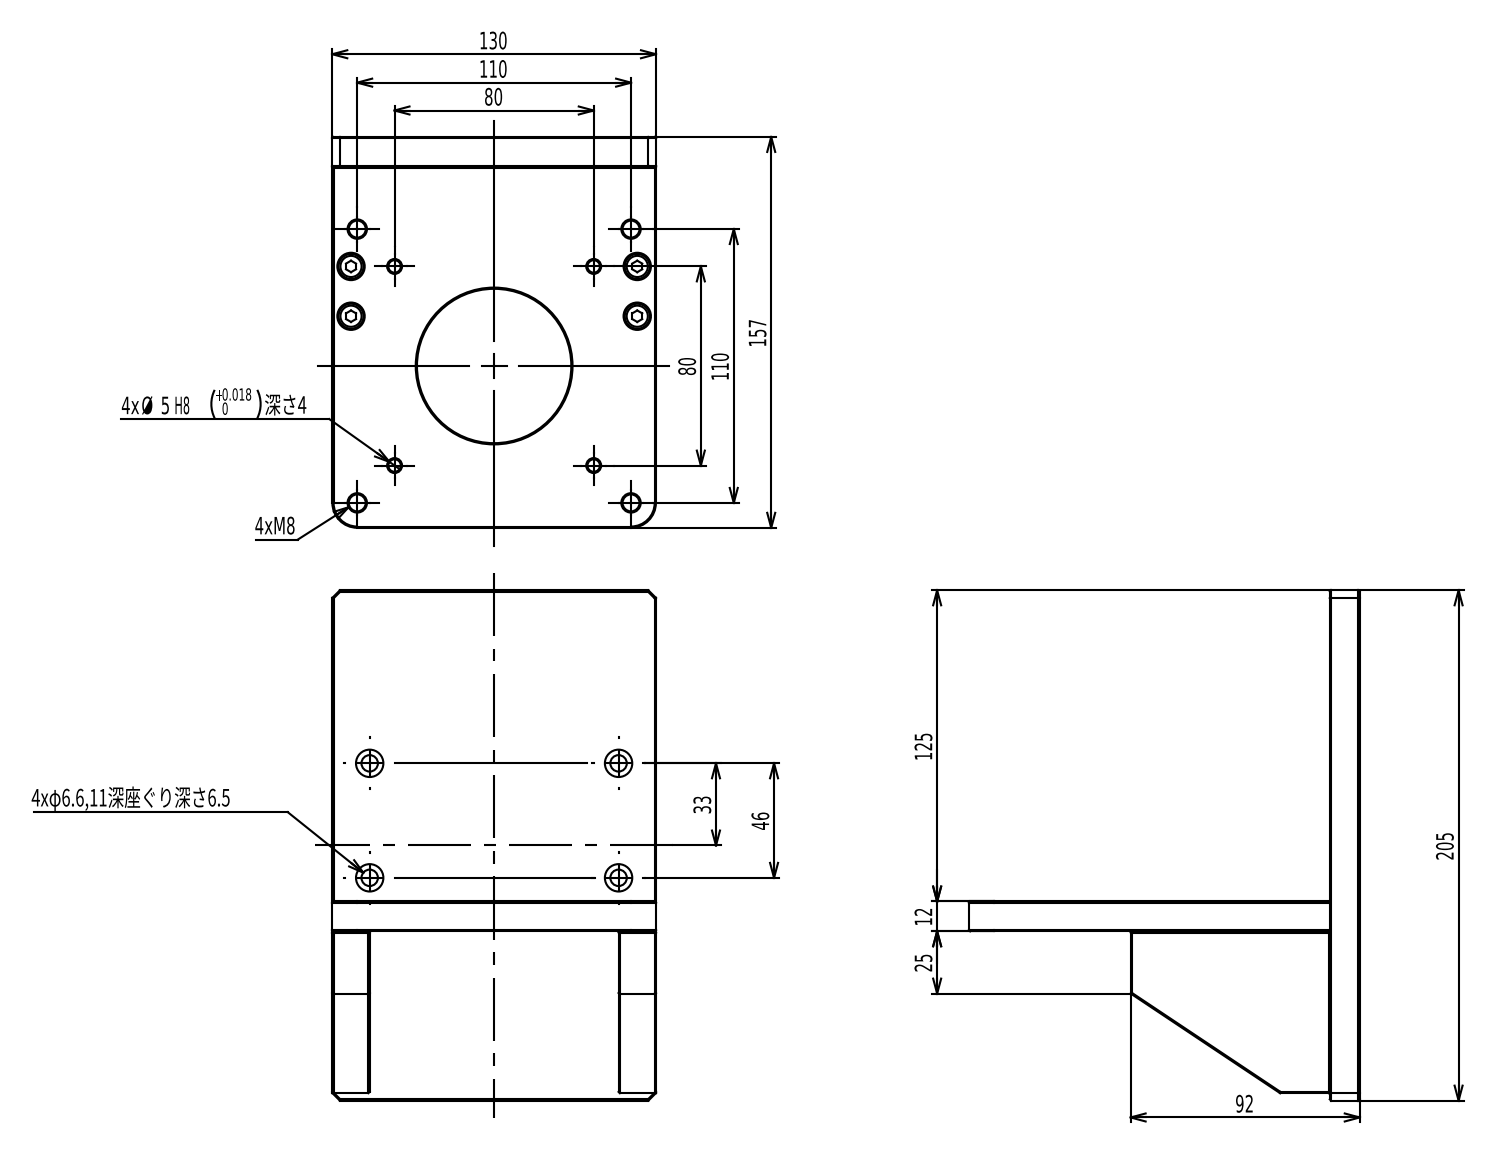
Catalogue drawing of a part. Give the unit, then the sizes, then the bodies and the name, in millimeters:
Units: millimetres
Overall size (bounding box): 205 × 157 × 130
Round holes (diameter × count): ⌀4.2 ×8, ⌀5.5 ×8, ⌀10 ×8, ⌀6.8 ×7, ⌀5 ×4, ⌀6.6 ×4, ⌀11 ×4, ⌀9 ×3, ⌀15 ×3, ⌀62 ×1
Round bosses / shafts (diameter × count): ⌀8.5 ×8, ⌀4.13 ×8, ⌀13 ×3, ⌀7 ×3
Partial cylindrical surfaces — rounded edges, fillets, slot ends (radius × count): R10 ×2
Main face-to-face distances: 12, 15, 115, 130, 100, 80, 137, 125, 68, 205
Hole centre spacings: 96.18, 80, 21.21, 56.57, 77.78, 110, 115, 134.35
Volume: 617 919 mm³ · Surface area: 138 544 mm²
Bodies: 15 solids, 487 faces (221 planar, 146 cylindrical, 120 other)
Part name (STEP PRODUCT): PDG130-7
STEP written by: SolidWorks 2020 (CONFIG_CONTROL_DESIGN)
